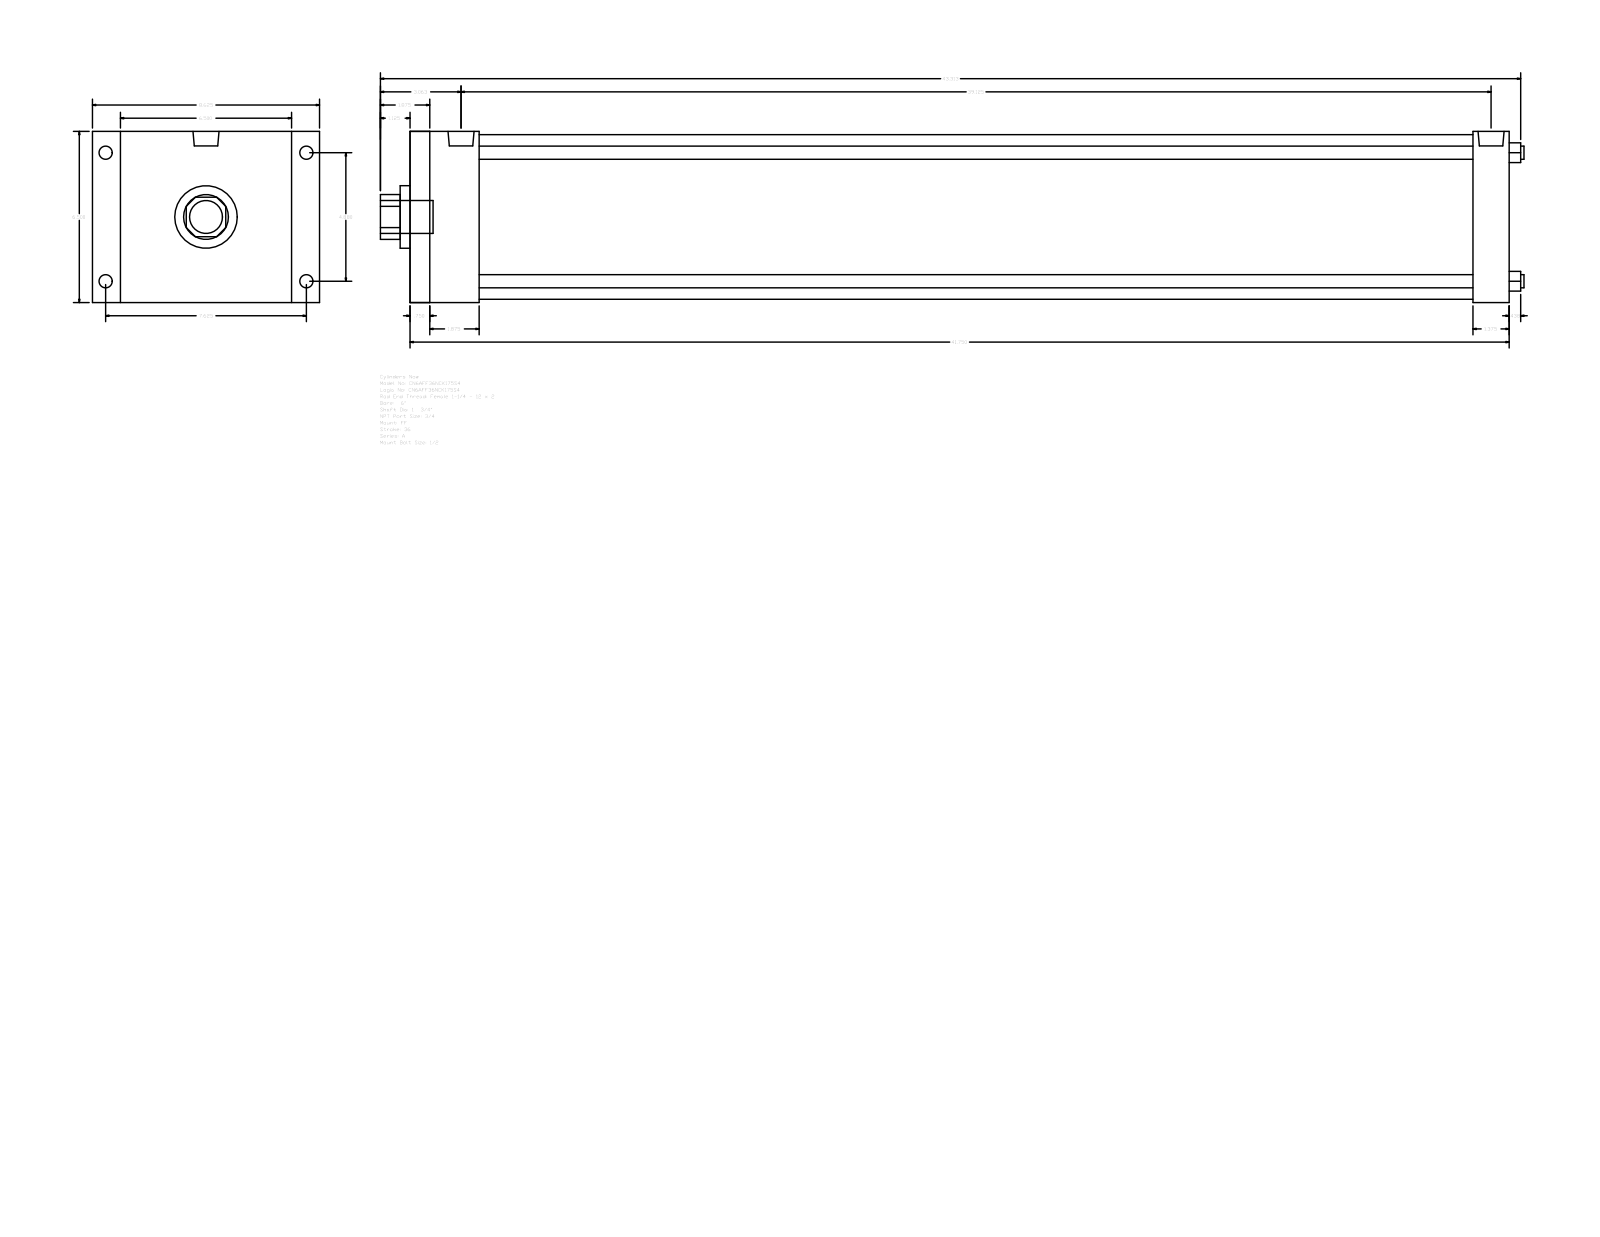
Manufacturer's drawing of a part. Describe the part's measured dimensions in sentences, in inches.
The part is named "A_FF__0600_1.75". Its 3-D file was written by "GSSL Pune (CONFIG_CONTROL_DESIGN)". It is 0 solids with 92 faces: 64 planar, 28 cylindrical and 0 other. Overall it measures 43.437 by 8.625 by 6.5 inches. Round holes: 4 of diameter 0.5, 1 of diameter 1.75, 1 of diameter 2.375, 1 of diameter 6.25. Round bosses or shafts: 4 of diameter 0.594, 4 of diameter 0.5, 2 of diameter 0.989, 1 of diameter 1.25. Partial cylindrical surfaces (rounded edges, fillets, slot ends): 1 of radius 0.852. The main face-to-face distances are 6.5, 41.75, 0.75, 41, 2.625, 1.875, 39.125, 40.375, 39.625, 37.75. The hole center spacings are 3.451, 4.88, 6.902.
